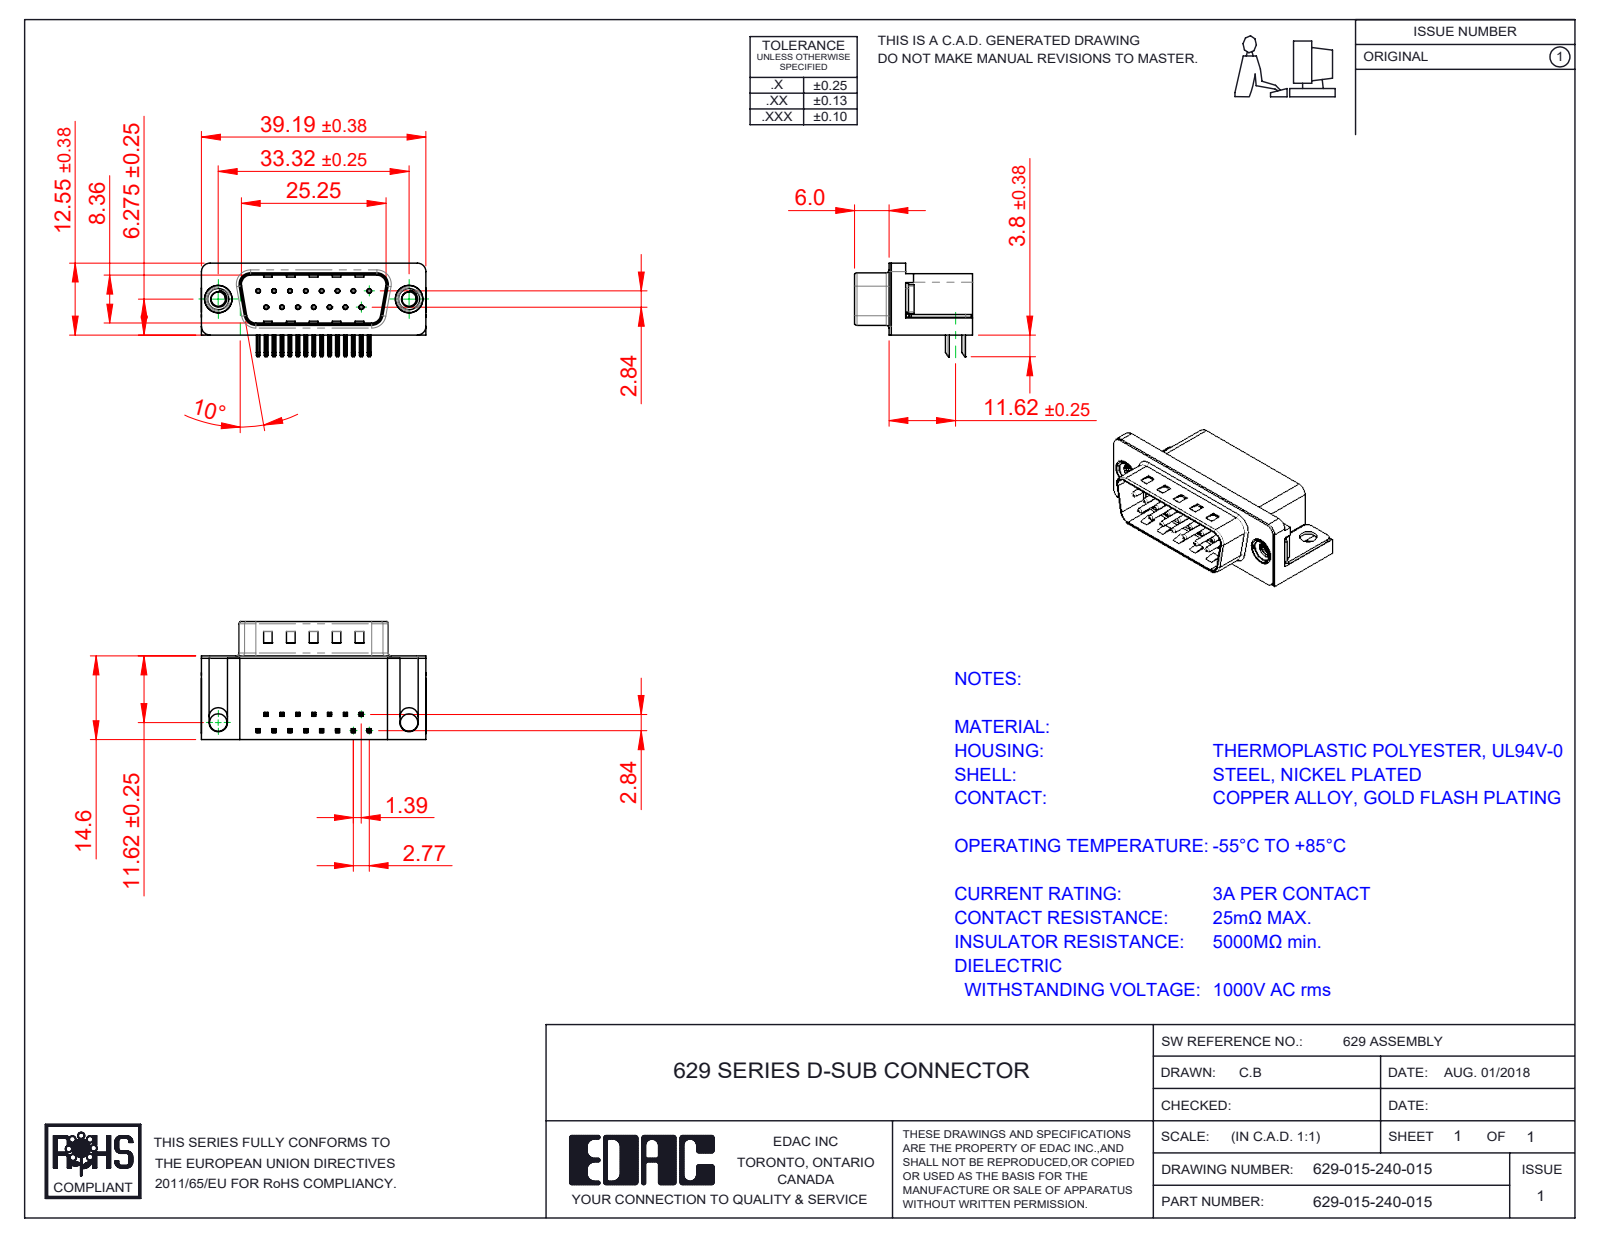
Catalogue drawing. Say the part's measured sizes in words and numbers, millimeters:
The part is named "629 Contact Bottom; 629 M3 Threaded Rivet; 629 Thru Hole Board Mount; 629-015-240-015 (+3 more)". Its 3-D file was written by "SolidWorks 2020 (CONFIG_CONTROL_DESIGN)". It is 21 solids with 1475 faces: 891 planar, 449 cylindrical and 135 other. Overall it measures 39.22 by 20.6 by 16.35 millimeters. Its volume is 5 070 cubic millimeters and its surface area 6 044 square millimeters. Round holes: 15 of diameter 0.35, 15 of diameter 0.8, 2 of diameter 2.5, 2 of diameter 3.05, 2 of diameter 4, 2 of diameter 4.8, 2 of diameter 5. Round bosses or shafts: 15 of diameter 0.75, 2 of diameter 4.9, 2 of diameter 4.75, 2 of diameter 3.9. Partial cylindrical surfaces (rounded edges, fillets, slot ends): 68 of radius 0.25, 30 of radius 0.12, 16 of radius 1, 9 of radius 0.5, 8 of radius 1.6, 6 of radius 1.5, 4 of radius 0.9, 4 of radius 2. The main face-to-face distances are 0.4, 14.2, 10.35, 2.1, 14.6, 10.46, 1.7, 10.86, 8.76, 0.5. The hole center spacings are 3.16, 2.77, 5.54, 8.31, 11.08, 5.03, 5.04, 7.48.
